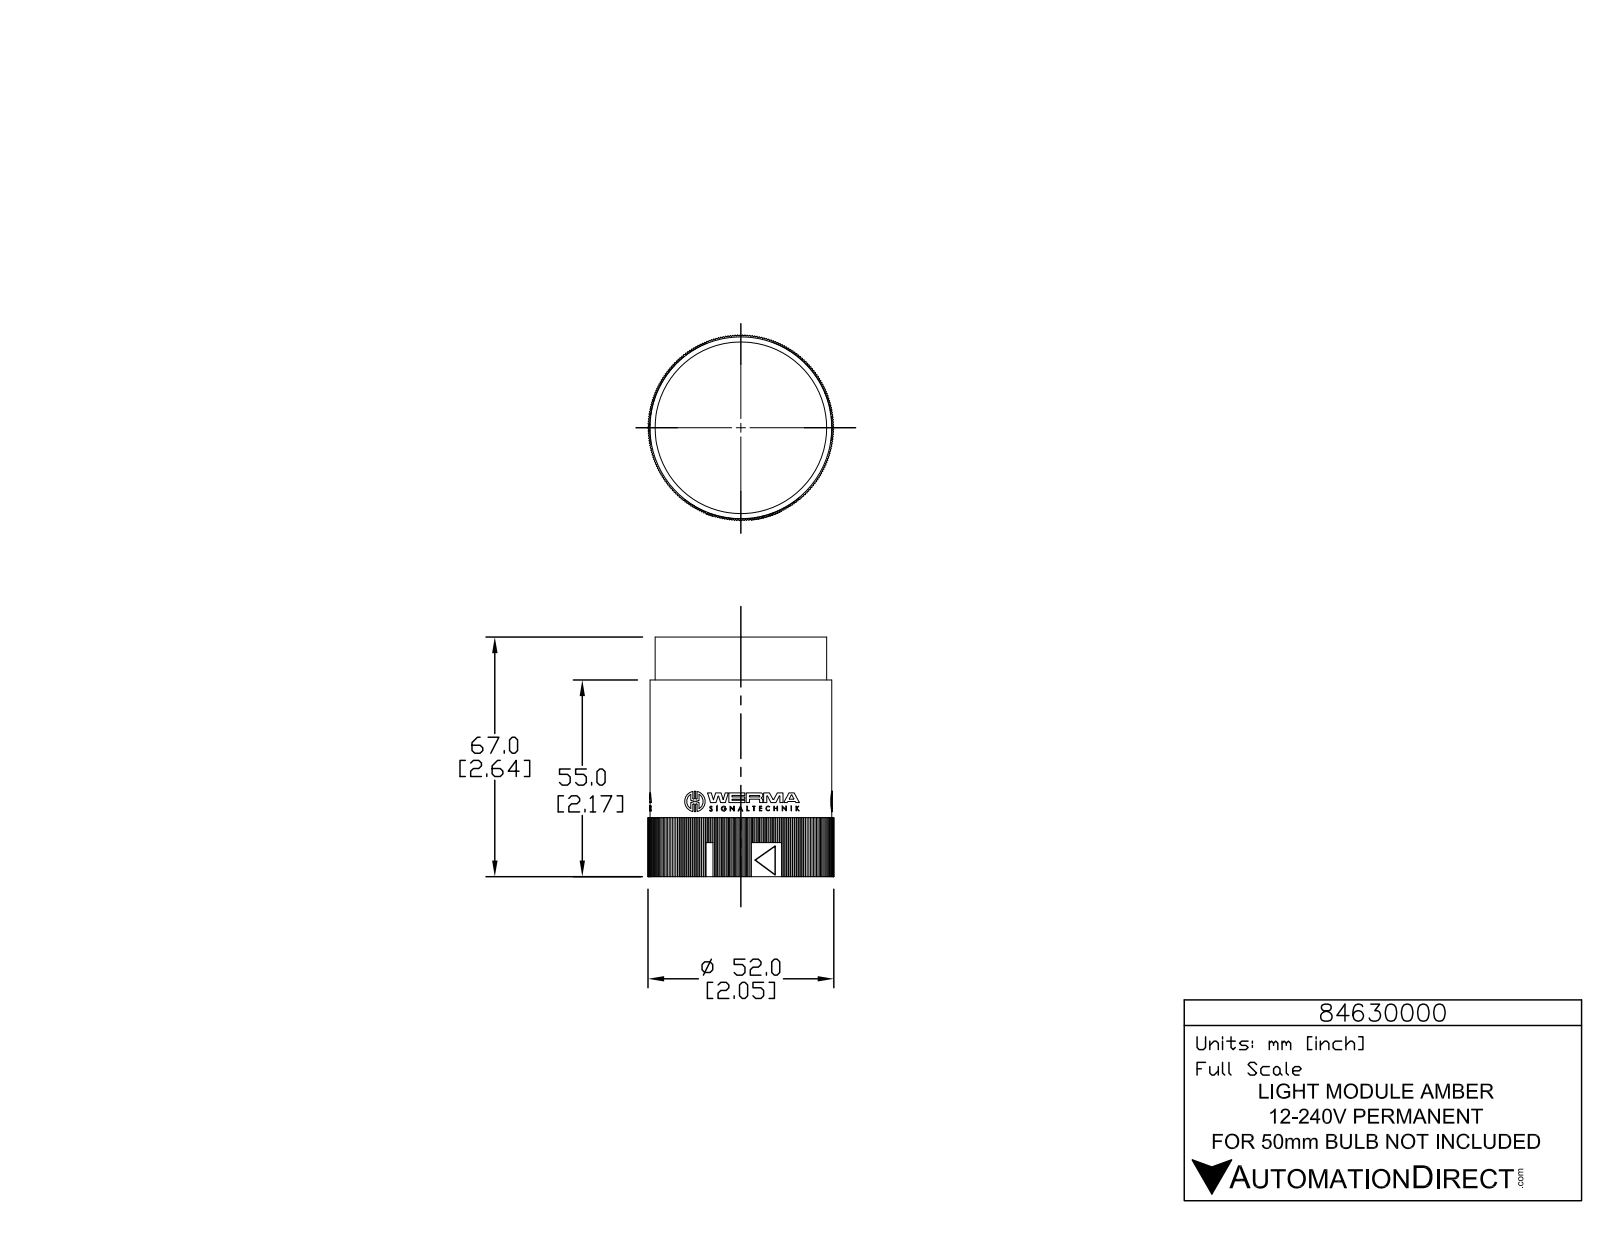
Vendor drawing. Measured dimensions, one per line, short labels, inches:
name: 84630000
written by: SolidWorks 2015 (AUTOMOTIVE_DESIGN)
unit: in
bodies: 1 solid, 1265 faces (1020 planar, 245 cylindrical, 0 other)
size: 2.638 × 2.047 × 2.047
volume: 6.873 in³; area: 27.62 in²
holes: 3× ⌀0.039, 1× ⌀1.898
bosses: 3× ⌀0.226, 3× ⌀0.056, 1× ⌀2.002, 1× ⌀1.89
rounds: 6× R0.008, 6× R0.008, 6× R0.008, 6× R0.131, 3× R0.004, 3× R0.005, 3× R0.008, 3× R0.008
face distances: 2.165, 1.428, 1.429, 1.429, 0.472, 2.638, 1.428, 1.428, 1.693, 1.988
